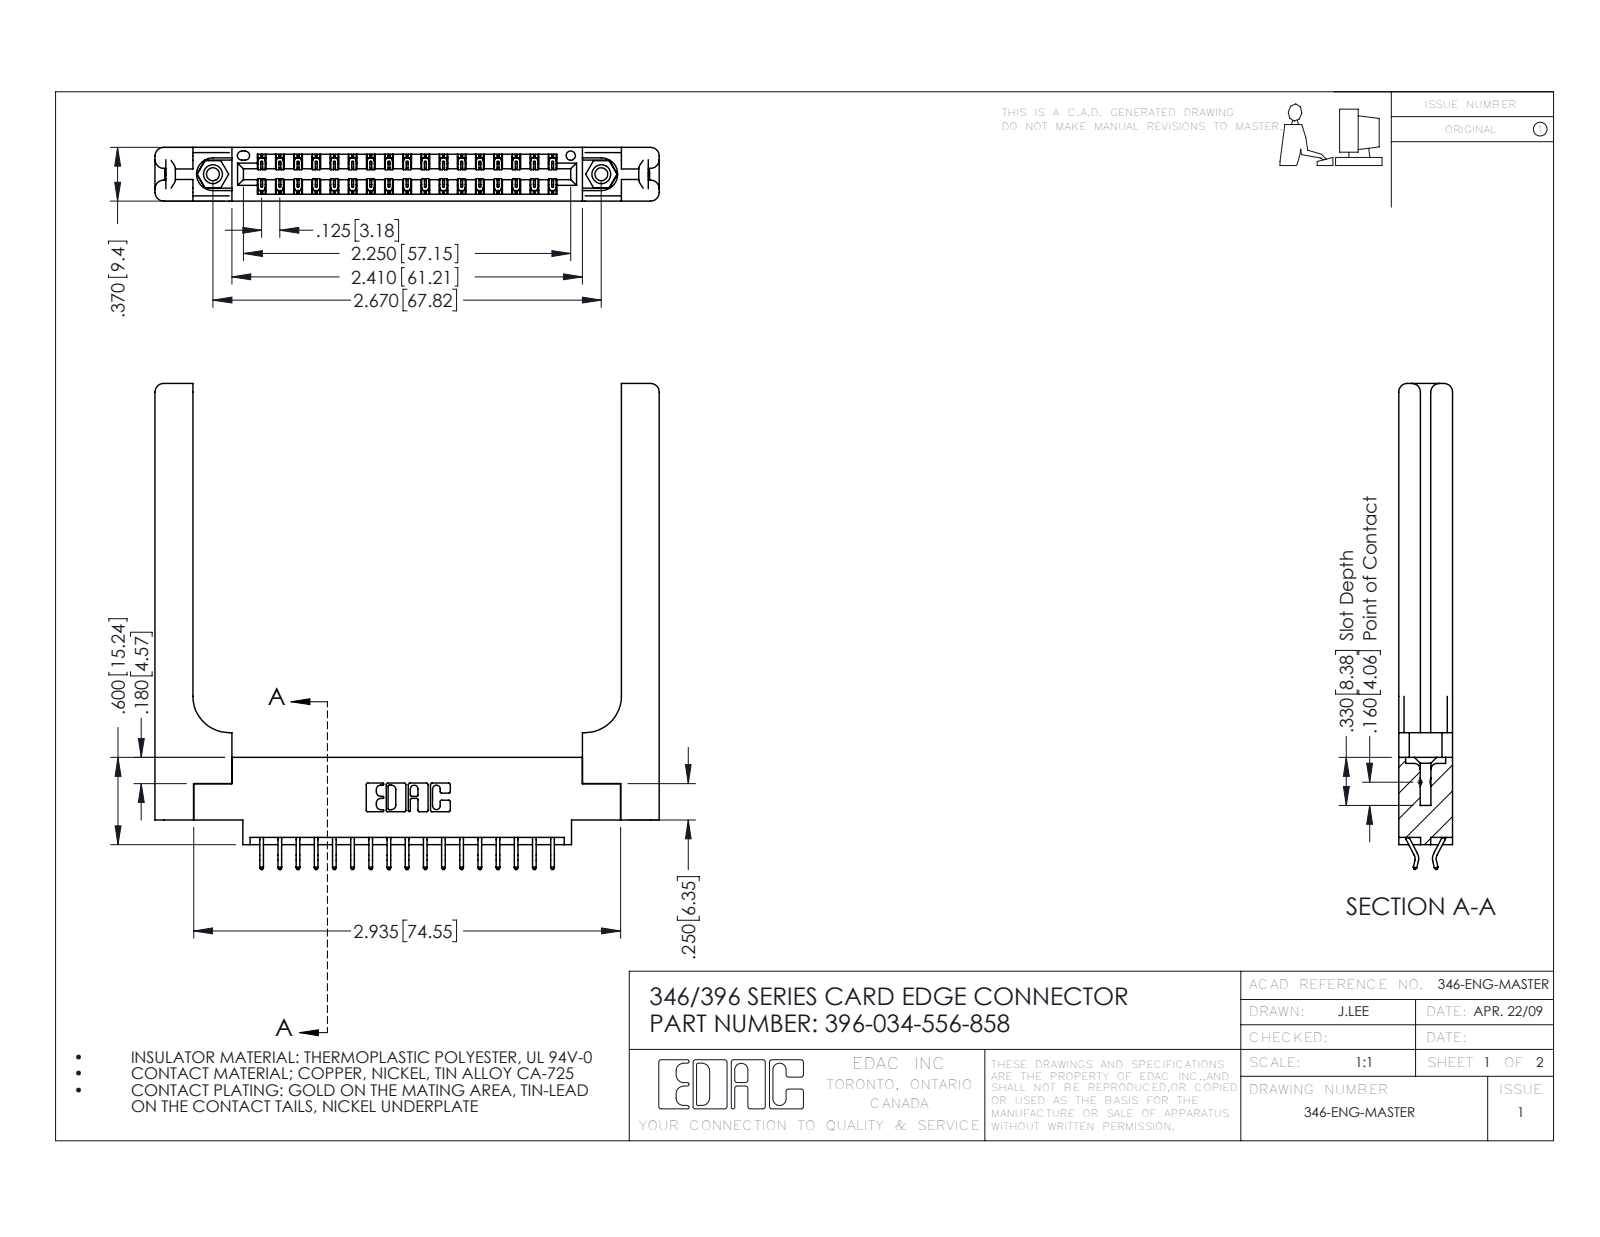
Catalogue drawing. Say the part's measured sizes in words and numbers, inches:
The part is named "396-034-556-858; 345-250-001_345-250-001-102; 346-220-058_345-220-058; 345-292-001_556 Tail (+1 more)". Its 3-D file was written by "SolidWorks 2016 (CONFIG_CONTROL_DESIGN)". It is 39 solids with 2354 faces: 1554 planar, 740 cylindrical and 60 other. Overall it measures 3.466 by 3.34 by 0.37 inches. Its volume is 0.96 cubic inches and its surface area 24.87 square inches. Round holes: 2 of diameter 0.089, 2 of diameter 0.125, 2 of diameter 0.156, 1 of diameter 0.064. Round bosses or shafts: 2 of diameter 0.155. Partial cylindrical surfaces (rounded edges, fillets, slot ends): 51 of radius 0.006, 22 of radius 0.01, 16 of radius 0.06, 6 of radius 0.007, 6 of radius 0.031, 3 of radius 0.026, 2 of radius 0.01, 2 of radius 0.014. The main face-to-face distances are 0.37, 0.15, 0.072, 0.148, 0.048, 0.322, 0.25, 0.102, 0.22, 0.173. The hole center spacings are 0.246, 2.463, 2.67.
